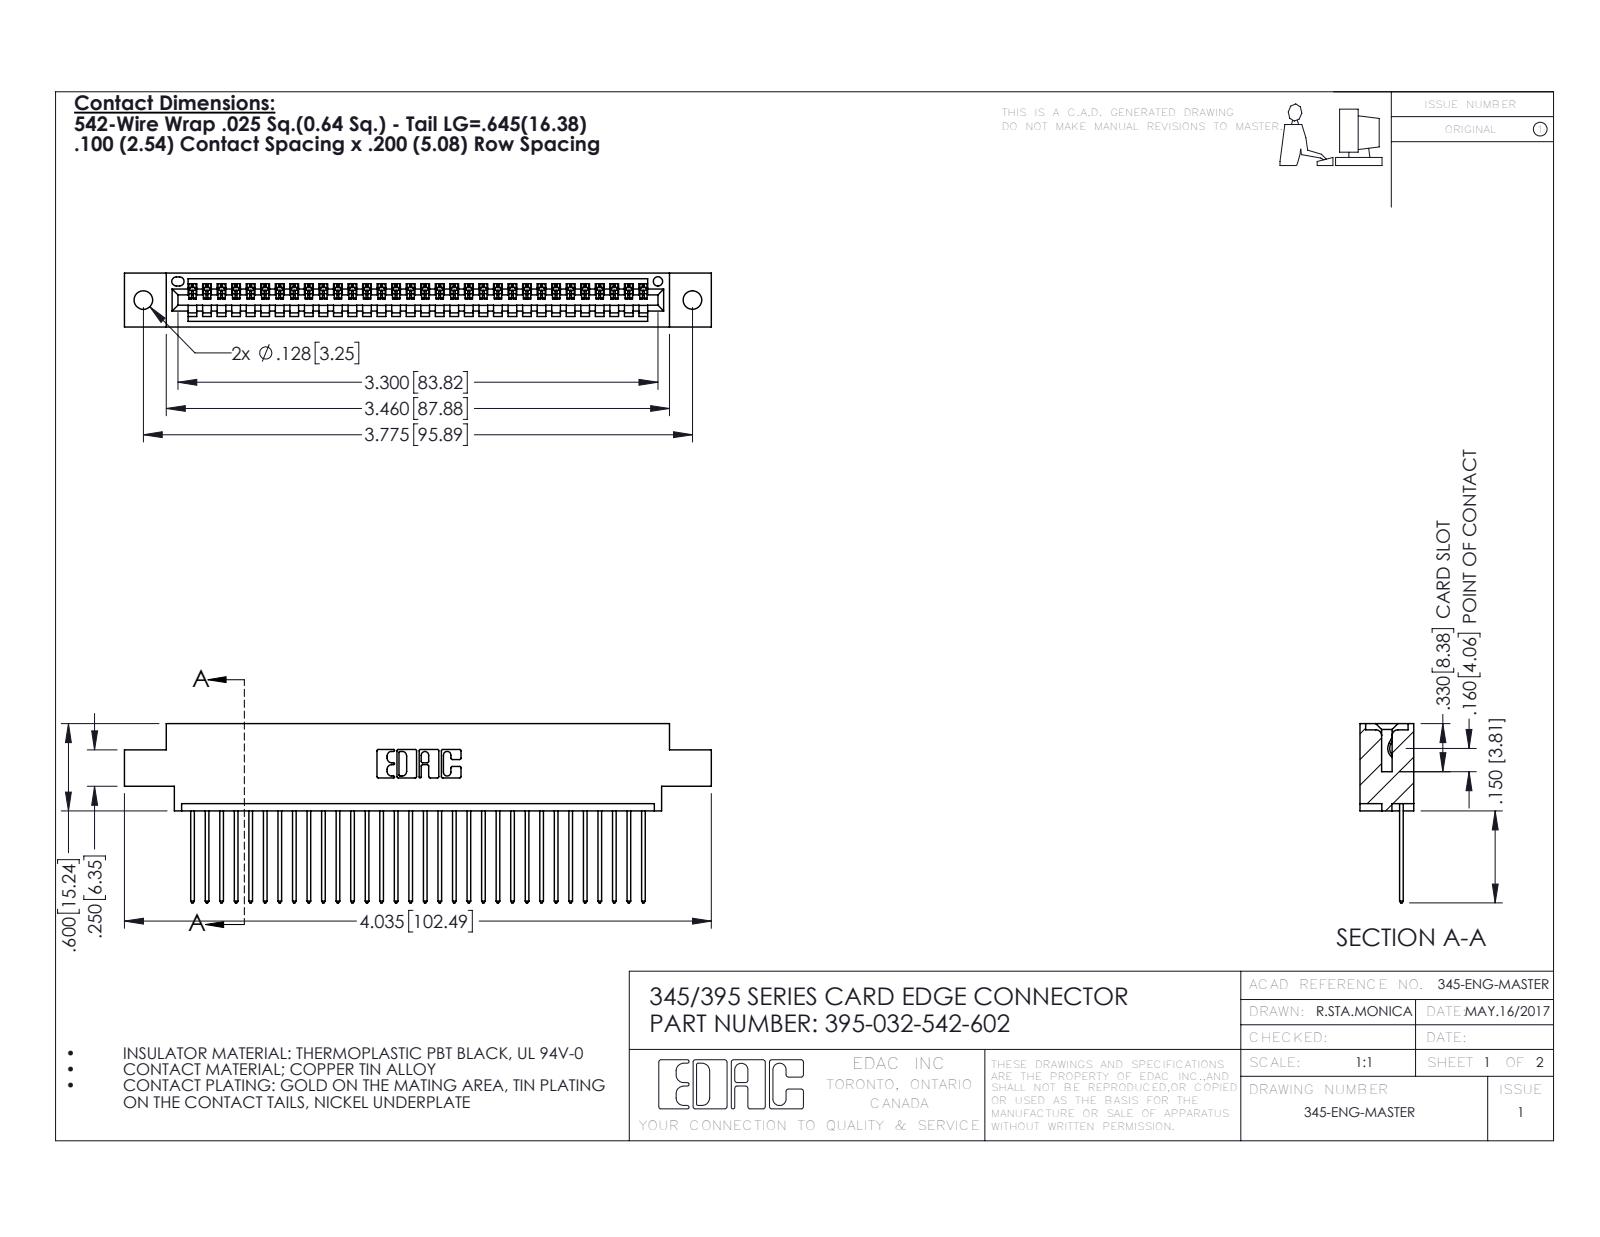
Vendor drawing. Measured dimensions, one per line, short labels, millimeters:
name: 345 Part_0.170 Offset - 0.128 Dia; 345-292-001_345-293-142; 395-032-542-602
written by: SolidWorks 2016 (CONFIG_CONTROL_DESIGN)
unit: mm
bodies: 33 solids, 1986 faces (1364 planar, 622 cylindrical, 0 other)
size: 102.5 × 31.3 × 9.4
volume: 9 570 mm³; area: 12 890 mm²
holes: 2× ⌀3.3, 1× ⌀1.6
rounds: 64× R0.2, 64× R0.3, 22× R0.3, 6× R0.2, 6× R0.8, 3× R0.7, 2× R0.8, 2× R1
face distances: 1.8, 7.6, 9.4, 2.5, 6.9, 0.6, 5.1, 5.7, 4.4, 3.8
hole spacings: 6.9, 89.9, 95.9
